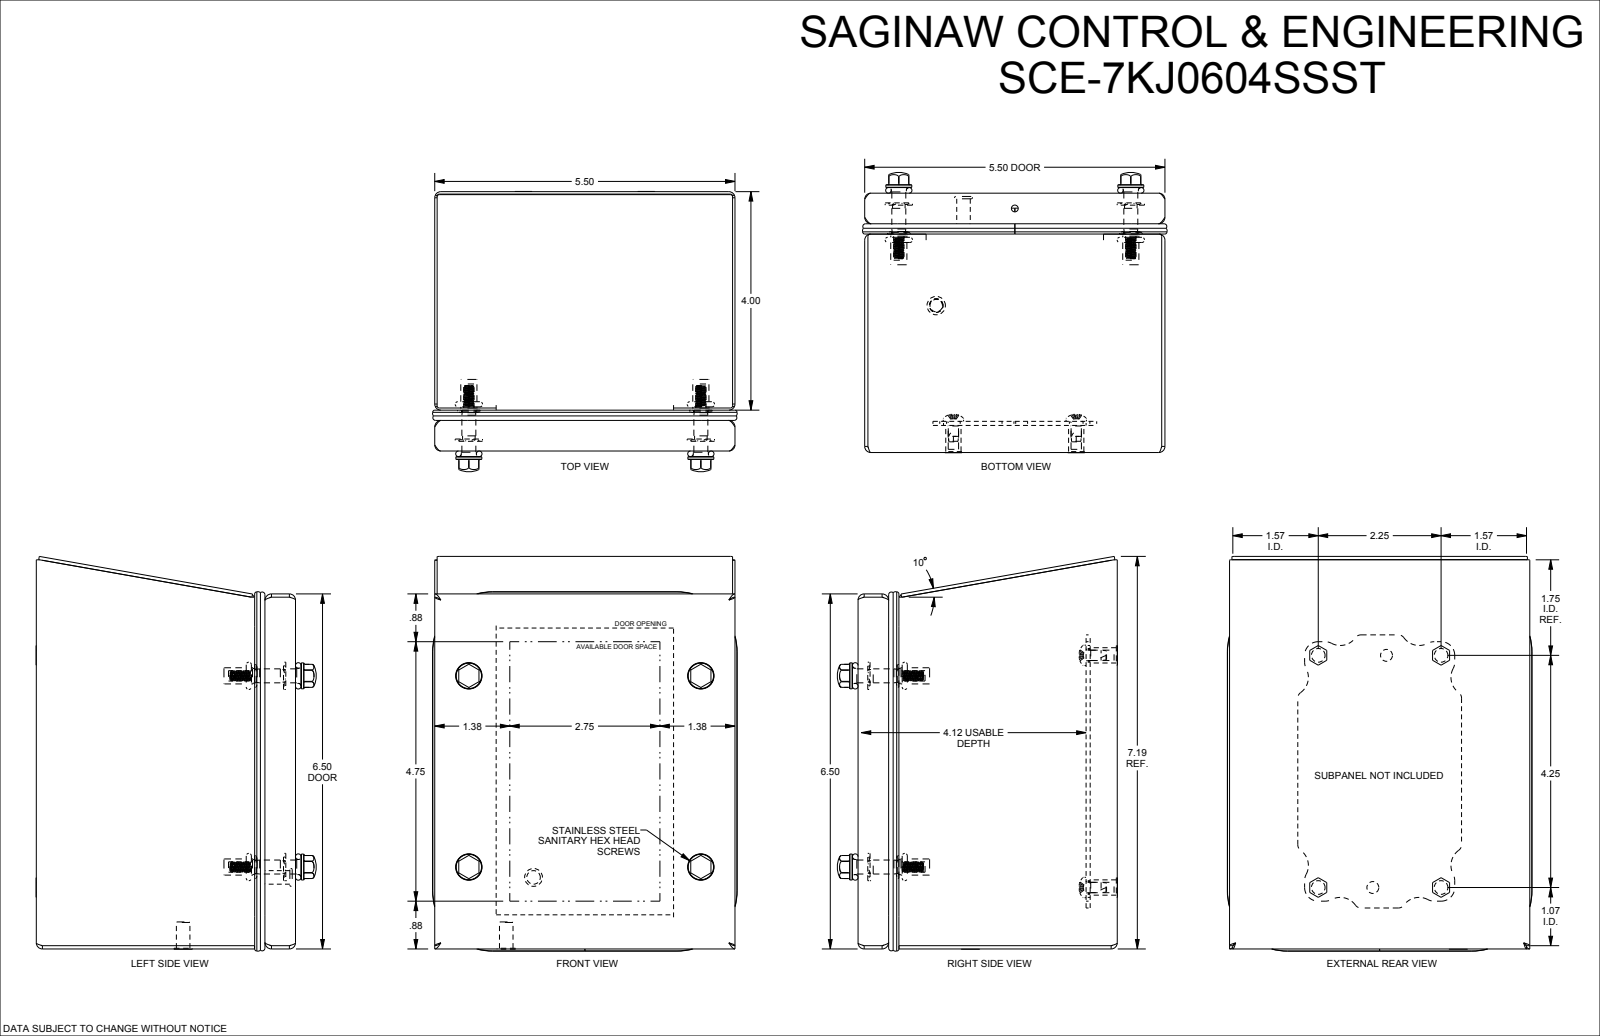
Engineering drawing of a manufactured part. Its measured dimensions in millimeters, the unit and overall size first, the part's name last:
Units: millimetres
Overall size (bounding box): 183.1 × 141.8 × 130.4
Round holes (diameter × count): ⌀4.8 ×8, ⌀7.1 ×8, ⌀6.4 ×4, ⌀6.9 ×4, ⌀8.1 ×4, ⌀9.3 ×4, ⌀5.5 ×2
Round bosses / shafts (diameter × count): ⌀12.7 ×4, ⌀12.1 ×4, ⌀9.5 ×4, ⌀7.5 ×4, ⌀7.1 ×4, ⌀6.5 ×4, ⌀5.8 ×4, ⌀4.8 ×4
Partial cylindrical surfaces — rounded edges, fillets, slot ends (radius × count): R1.3 ×26, R2.8 ×26, R0.5 ×20, R3.2 ×12, R6.4 ×12, R8.7 ×8, R0.1 ×4, R0.3 ×4
Main face-to-face distances: 1.5, 119.1, 138.2, 117.6, 100.1, 19, 120.6, 139.7, 136.7, 101.6
Hole centre spacings: 88.9, 128.4, 27.1, 83.1, 101.7, 107.8, 108, 57.2
Volume: 313 800 mm³ · Surface area: 361 700 mm²
Bodies: 31 solids, 991 faces (349 planar, 309 cylindrical, 333 other)
Part name (STEP PRODUCT): SCE-7KJ0604SSST
STEP written by: SolidWorks 2021 (AUTOMOTIVE_DESIGN)
